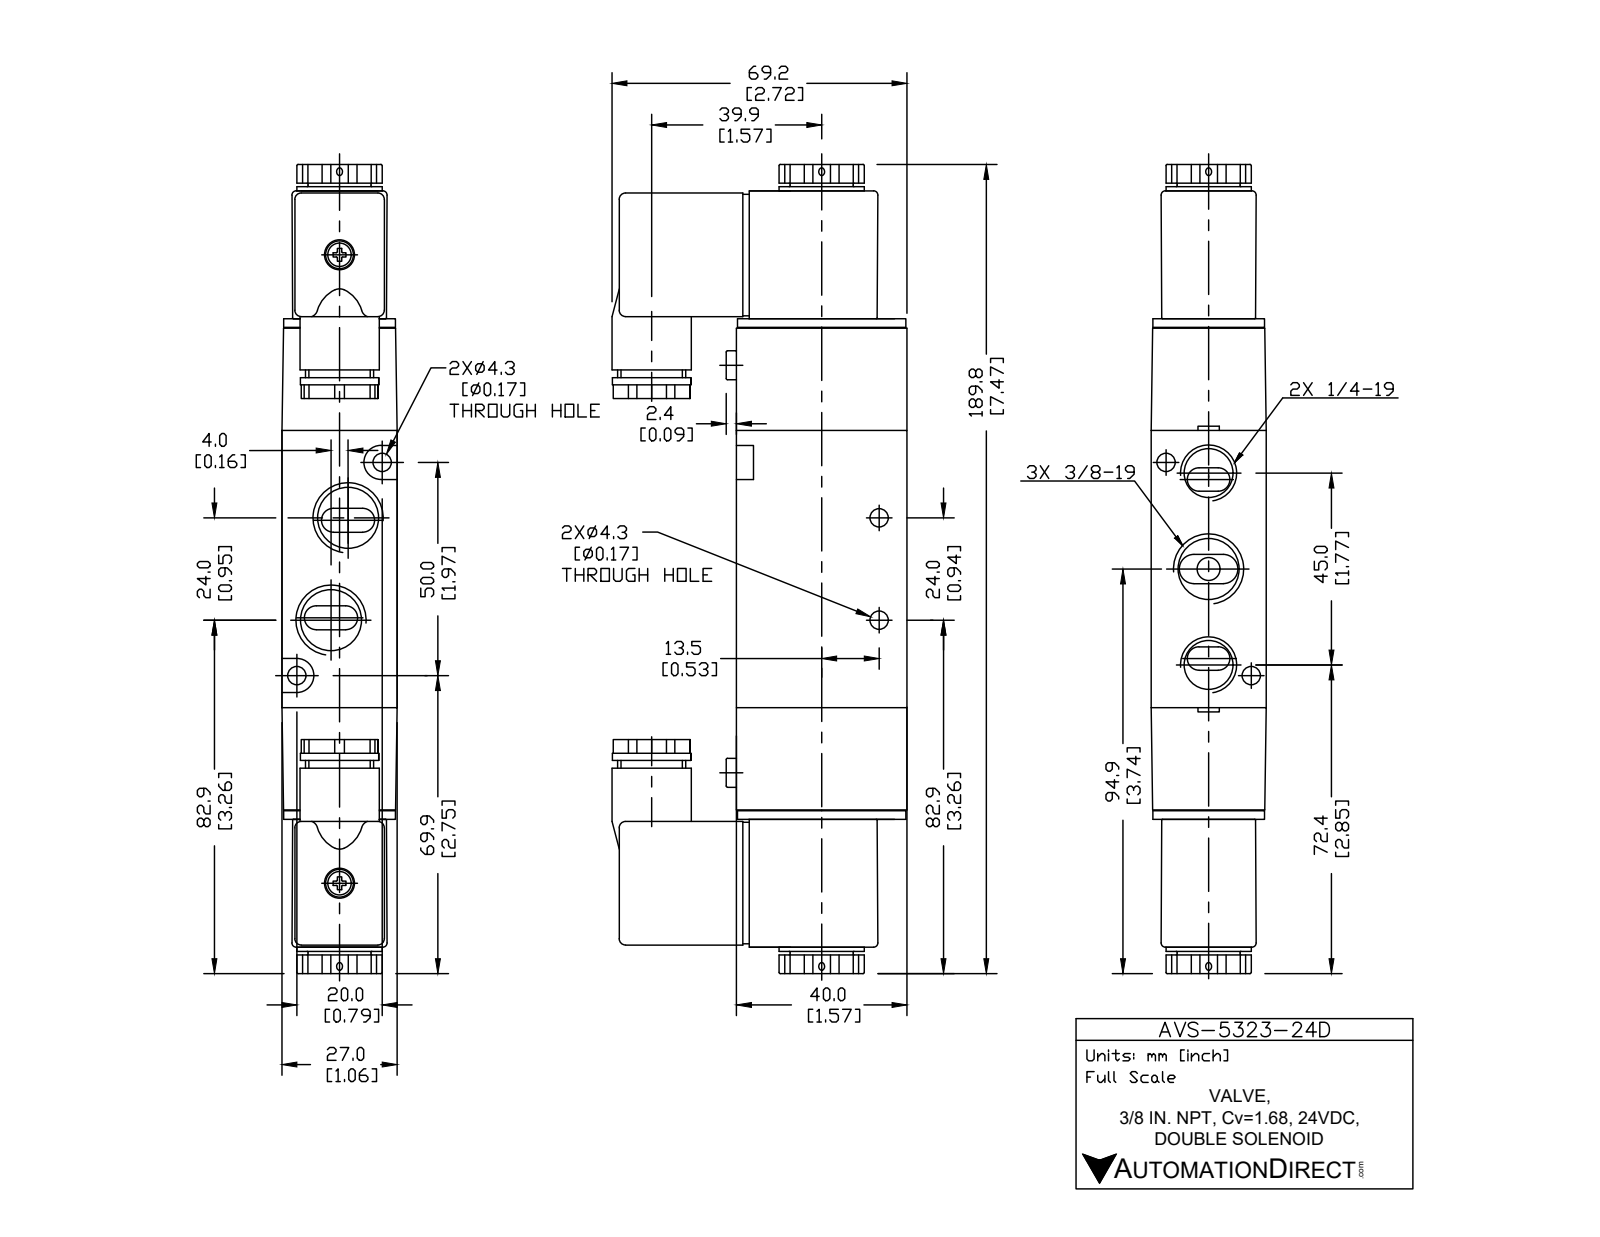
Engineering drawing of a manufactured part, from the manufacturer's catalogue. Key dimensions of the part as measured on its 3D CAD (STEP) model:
Part name (STEP PRODUCT): AVS-5323-24D
STEP written by: SolidWorks 2021 (CONFIG_CONTROL_DESIGN)
Units: millimetres
Bodies: 5 solids, 272 faces (127 planar, 111 cylindrical, 34 other)
Overall size (bounding box): 189.8 × 69.2 × 27
Volume: 201 178 mm³ · Surface area: 43 429 mm²
Round holes (diameter × count): ⌀4.3 ×4, ⌀14.27 ×3, ⌀11.13 ×2, ⌀9.3 ×1
Round bosses / shafts (diameter × count): ⌀6.7 ×2, ⌀20 ×1, ⌀18.6 ×1, ⌀18.4 ×1, ⌀16 ×1, ⌀14.8 ×1
Partial cylindrical surfaces — rounded edges, fillets, slot ends (radius × count): R1.5 ×18, R1 ×10, R3 ×10, R0.5 ×8, R3.95 ×2
Main face-to-face distances: 27, 3, 24, 40, 65, 23.06, 21, 29.5, 0.5, 147.4
Hole centre spacings: 10.31, 10.69, 12.17, 15.26, 22.5, 26.93, 34.56, 38.9
